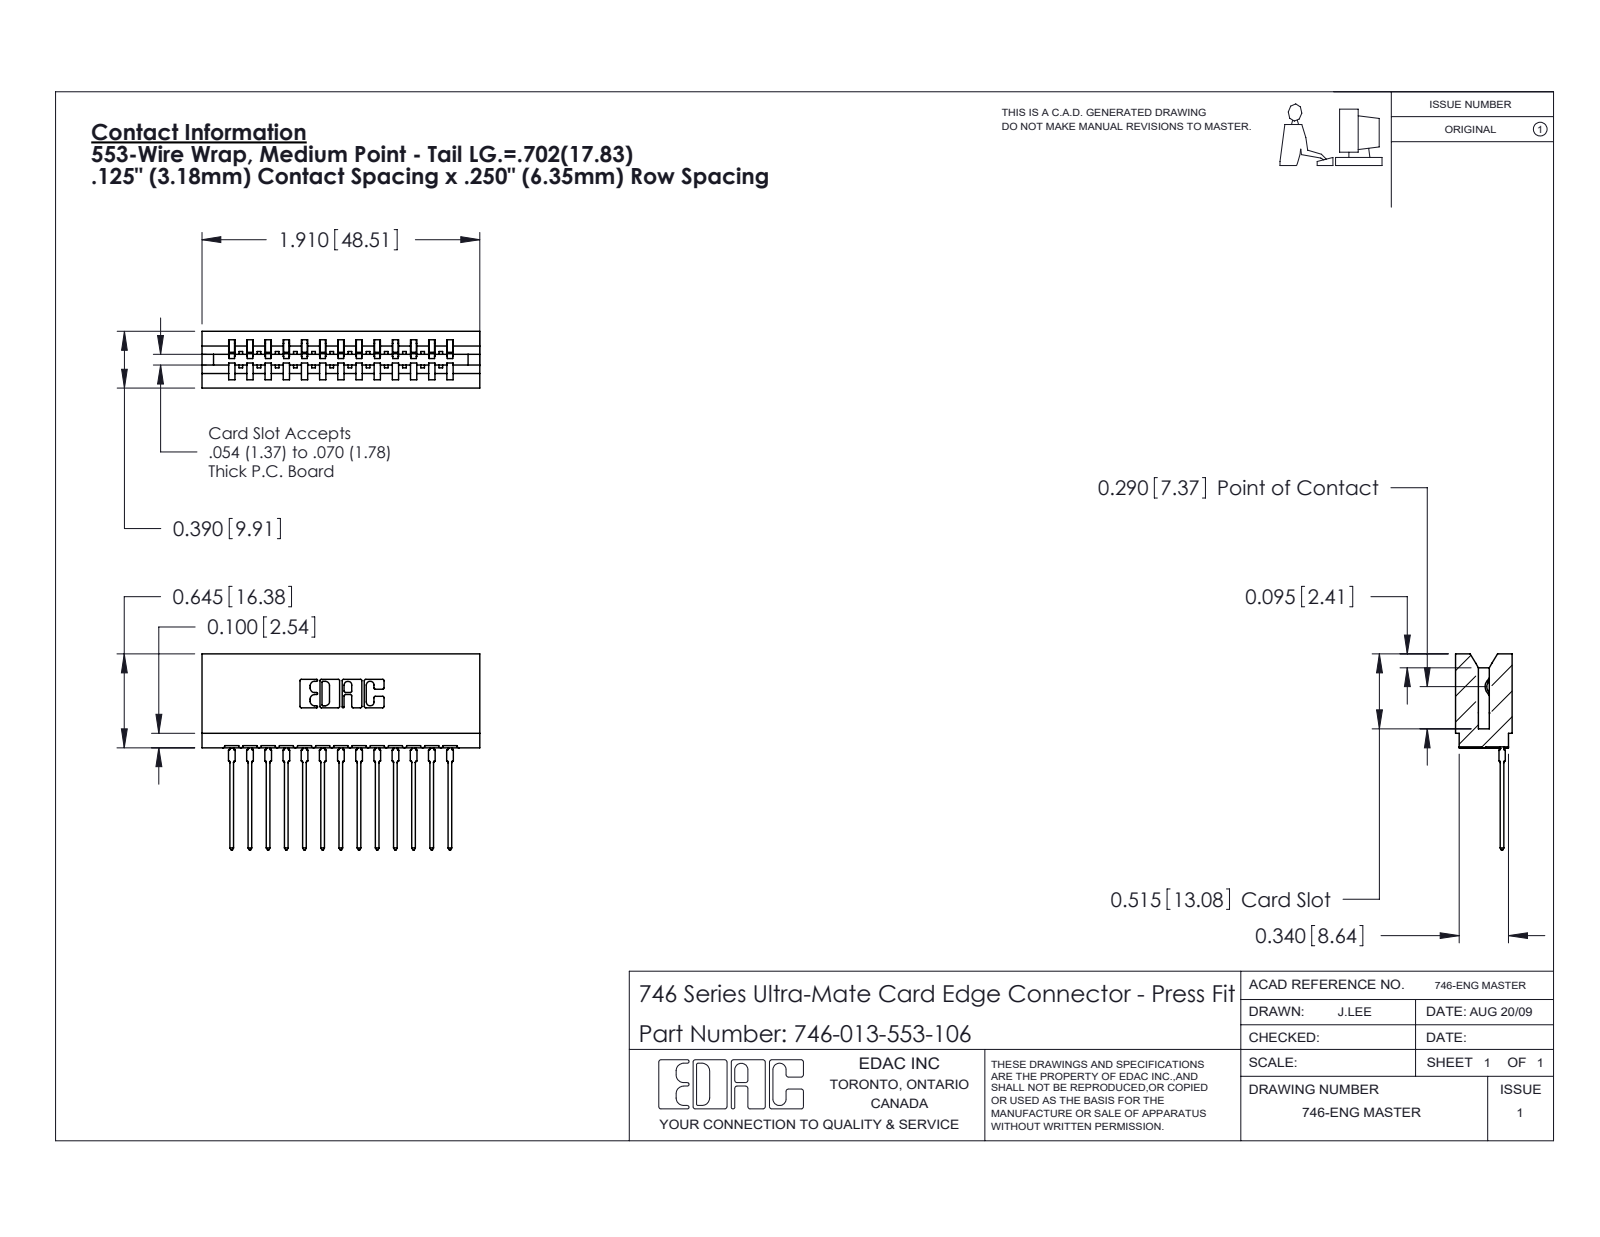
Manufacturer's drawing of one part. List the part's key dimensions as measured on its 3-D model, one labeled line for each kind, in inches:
Part name (STEP PRODUCT): 746-013-553-106; 746-292-001_553; 746 Part_.515 Slot Depth - 06
STEP written by: SolidWorks 2020 (CONFIG_CONTROL_DESIGN)
Units: inches
Bodies: 14 solids, 1502 faces (875 planar, 289 cylindrical, 338 other)
Overall size (bounding box): 1.91 × 1.346 × 0.39
Volume: 0.323 in³ · Surface area: 11.8 in²
Partial cylindrical surfaces — rounded edges, fillets, slot ends (radius × count): R0.021 ×26, R0.01 ×22, R0.015 ×14, R0.007 ×6, R0.031 ×6, R0.005 ×4, R0.011 ×4, R0.026 ×3
Main face-to-face distances: 0.25, 0.333, 0.057, 0.5, 0.39, 0.125, 0.125, 0.025, 0.083, 0.307
